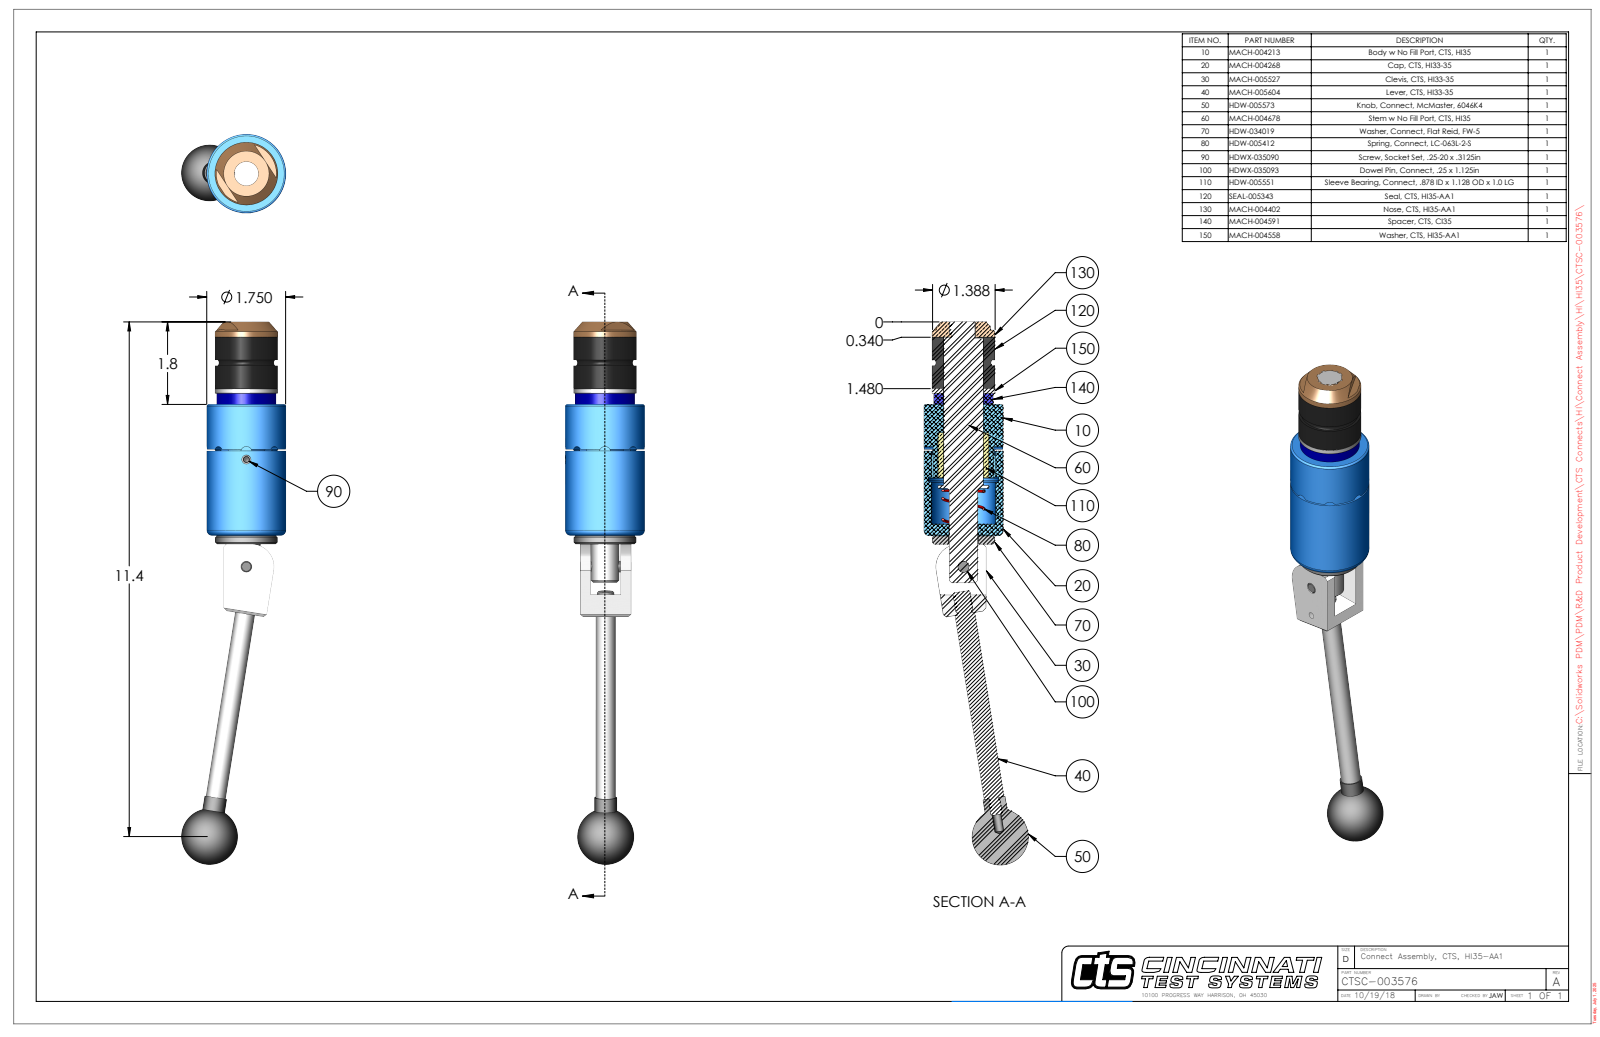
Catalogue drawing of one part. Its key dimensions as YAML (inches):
part_name: "CTSC-003576"
step_written_by: "SolidWorks 2023 (AUTOMOTIVE_DESIGN)"
units: inches
bodies: {solids: 10, faces: 261, planar: 96, cylindrical: 104, other: 61}
overall_size: [12.039, 2.312, 1.75]
volume: 12.78
surface_area: 76.67
round_holes:
  - {diameter: 0.201, count: 2}
  - {diameter: 0.15, count: 1}
  - {diameter: 0.249, count: 1}
  - {diameter: 0.251, count: 1}
  - {diameter: 0.313, count: 1}
  - {diameter: 0.531, count: 1}
  - {diameter: 0.635, count: 1}
  - {diameter: 0.656, count: 1}
  - {diameter: 0.875, count: 1}
  - {diameter: 0.876, count: 1}
  - {diameter: 0.885, count: 1}
  - {diameter: 1.419, count: 1}
round_bosses_or_shafts:
  - {diameter: 0.25, count: 2}
  - {diameter: 1.75, count: 1}
  - {diameter: 1.388, count: 1}
  - {diameter: 1.38, count: 1}
  - {diameter: 1.312, count: 1}
  - {diameter: 0.871, count: 1}
  - {diameter: 0.869, count: 1}
  - {diameter: 0.625, count: 1}
partial_cylinders:
  - {radius: 0.125, count: 4}
  - {radius: 0.029, count: 2}
  - {radius: 0.5, count: 1}
  - {radius: 0.695, count: 1}
  - {radius: 0.825, count: 1}
face_to_face_distances: [2.912, 1.49, 4.402, 1.14, 0.35, 3.262, 1.25, 0.11, 0.24, 3.152]
hole_center_spacings: [0.74, 2.376, 3.116]
